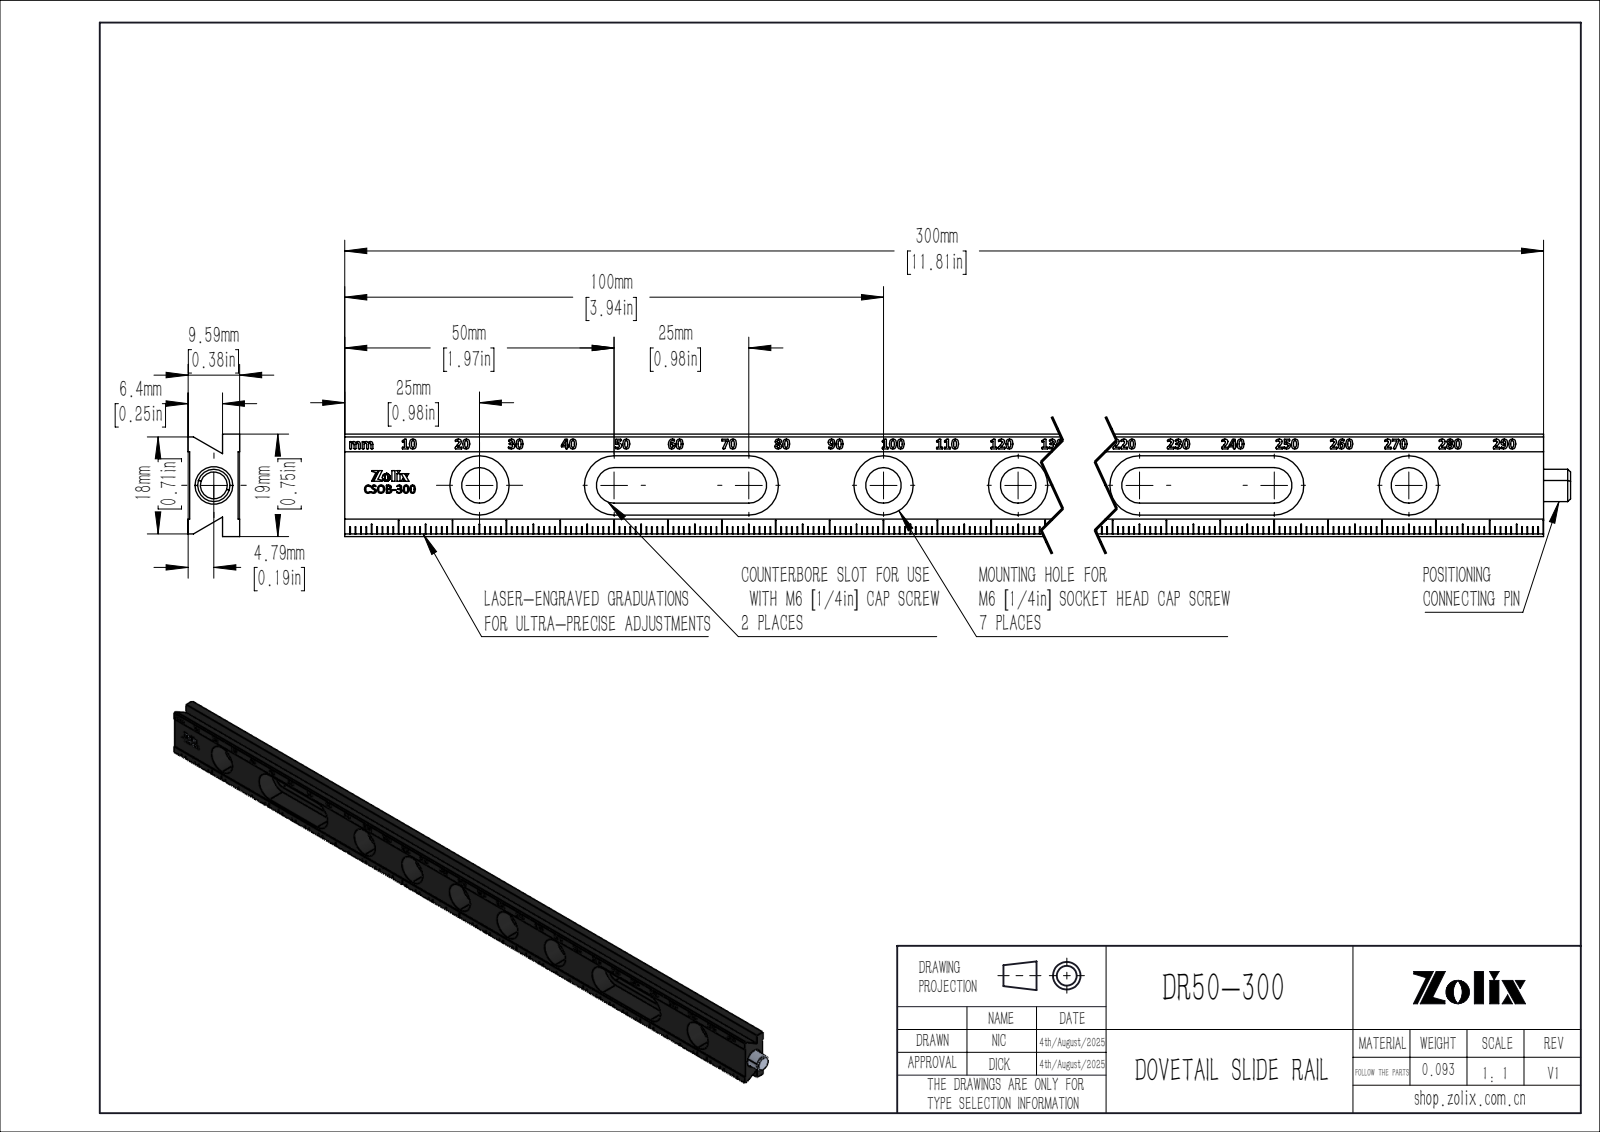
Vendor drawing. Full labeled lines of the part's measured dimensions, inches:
Part name (STEP PRODUCT): CSOB-300
STEP written by: SolidWorks 2020 (CONFIG_CONTROL_DESIGN)
Units: inches
Bodies: 2 solids, 1694 faces (1564 planar, 42 cylindrical, 88 other)
Overall size (bounding box): 12.008 × 0.748 × 0.378
Volume: 2.103 in³ · Surface area: 35.33 in²
Round holes (diameter × count): ⌀0.26 ×7, ⌀0.433 ×7, ⌀0.236 ×1
Partial cylindrical surfaces — rounded edges, fillets, slot ends (radius × count): R0.13 ×4, R0.217 ×4
Main face-to-face distances: 0.366, 0.354, 0.24, 0.114, 0.126, 0.252, 0.378, 0.087, 0.748, 0.268
Hole centre spacings: 0.984, 2.953, 1.969, 3.937, 4.921, 5.906, 6.89, 9.843
